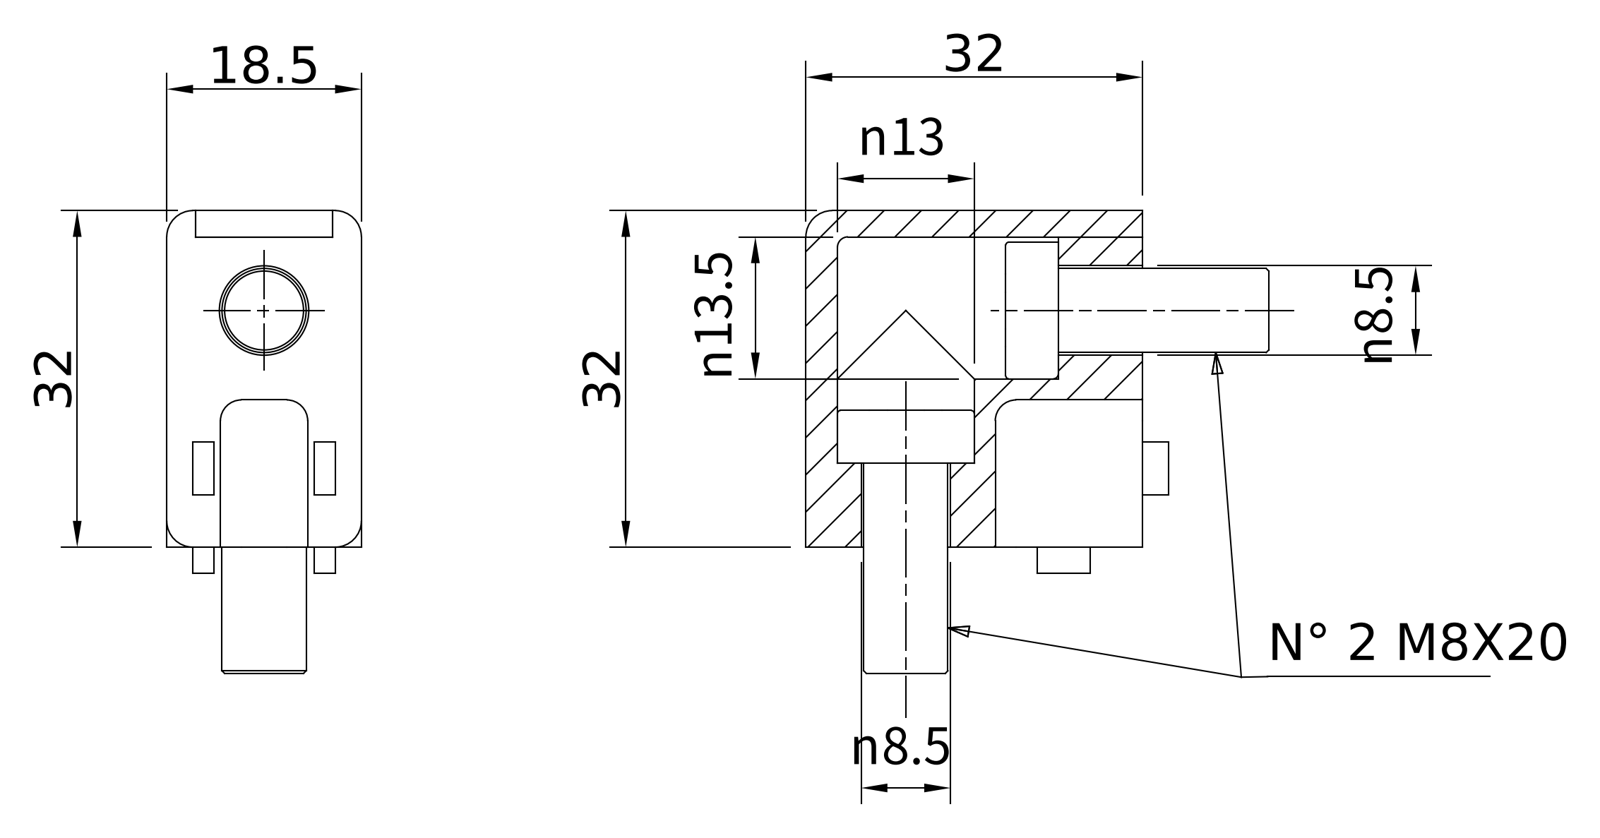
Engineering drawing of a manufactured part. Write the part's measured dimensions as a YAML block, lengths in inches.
part_name: "CGIPR0000101"
step_written_by: "Autodesk Inventor 2019 (AUTOMOTIVE_DESIGN)"
units: inches
bodies: {solids: 4, faces: 115, planar: 71, cylindrical: 33, other: 11}
overall_size: [1.732, 1.732, 0.728]
volume: 0.907
surface_area: 15.03
round_holes:
  - {diameter: 0.079, count: 2}
  - {diameter: 0.098, count: 2}
  - {diameter: 0.335, count: 2}
  - {diameter: 0.512, count: 2}
round_bosses_or_shafts:
  - {diameter: 0.315, count: 2}
partial_cylinders:
  - {radius: 0.079, count: 5}
  - {radius: 0.098, count: 5}
  - {radius: 0.02, count: 2}
  - {radius: 0.039, count: 1}
face_to_face_distances: [0.728, 1.26, 0.108, 0.62, 0.512, 0.098, 0.315, 0.945, 1.161, 0.201]
hole_center_spacings: [0.343, 0.754, 1.034, 1.093, 0.315, 0.394]
